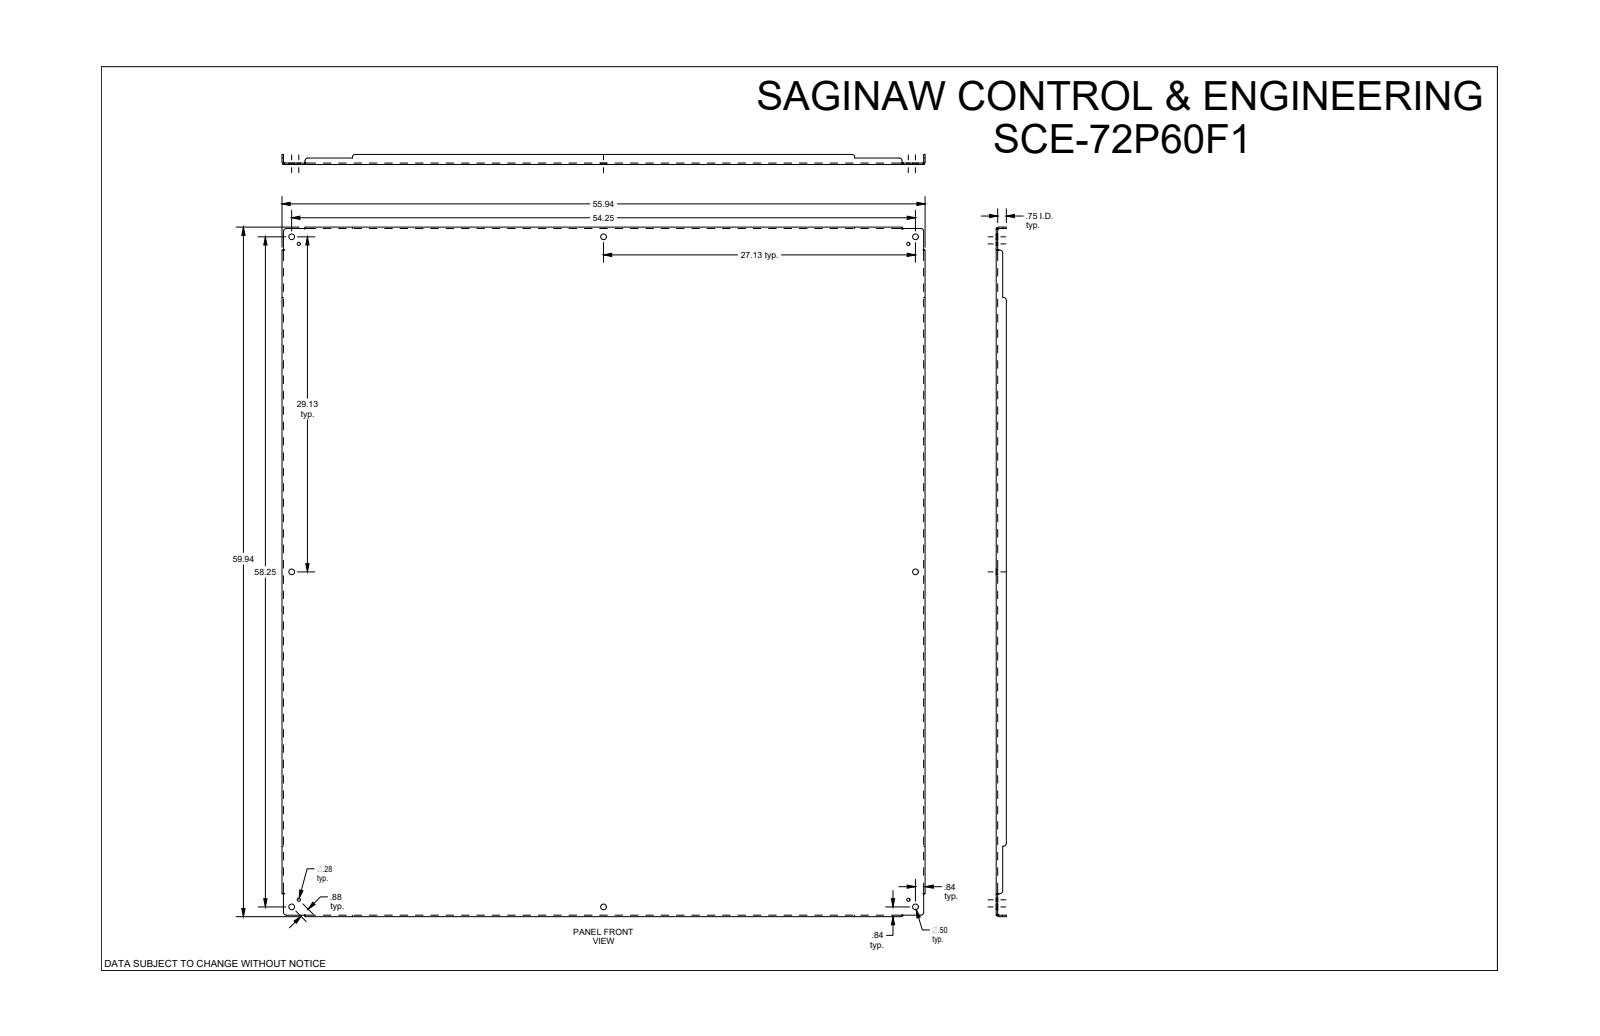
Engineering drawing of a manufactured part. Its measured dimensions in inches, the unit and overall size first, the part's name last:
Units: inches
Overall size (bounding box): 59.938 × 55.938 × 0.875
Round holes (diameter × count): ⌀0.5 ×8, ⌀0.281 ×4
Partial cylindrical surfaces — rounded edges, fillets, slot ends (radius × count): R0.25 ×12, R0.112 ×4, R0.237 ×4
Main face-to-face distances: 0.125, 0.125, 55.813, 59.813, 55.687, 55.938, 59.687, 59.938, 0.75, 0.875
Hole centre spacings: 0.875, 26.513, 27.125, 28.513, 29.125, 39.8, 53.635, 57.634
Volume: 435.5 in³ · Surface area: 7 000 in²
Bodies: 1 solid, 110 faces (46 planar, 40 cylindrical, 24 other)
Part name (STEP PRODUCT): SCE-72P60F1
STEP written by: SolidWorks 2019 (CONFIG_CONTROL_DESIGN)
